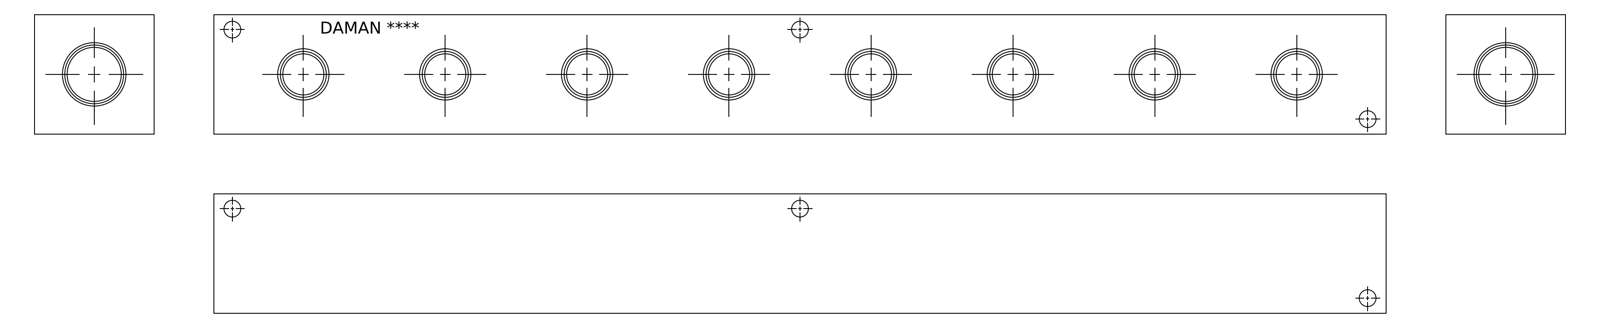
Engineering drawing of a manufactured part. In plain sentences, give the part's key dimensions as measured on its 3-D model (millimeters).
The part is named "Part_+H0000808P_3D". Its 3-D file was written by "Autodesk Inventor 2019 (AUTOMOTIVE_DESIGN)". It is 1 solid with 369 faces: 213 planar, 32 cylindrical and 124 other. Overall it measures 498.48 by 50.8 by 50.8 millimeters. Its volume is 1 205 000 cubic millimeters and its surface area 124 395 square millimeters. Round holes: 8 of diameter 17.48, 8 of diameter 21.59, 6 of diameter 7.14, 1 of diameter 23.01, 1 of diameter 26.92. The main face-to-face distances are 50.8, 498.48, 35.43, 15.37, 15.85, 482.63, 466.78, 49.8, 14.37, 1. The hole center spacings are 120.65, 60.33, 180.98, 241.3, 60.32, 301.63, 35.66, 35.69.
